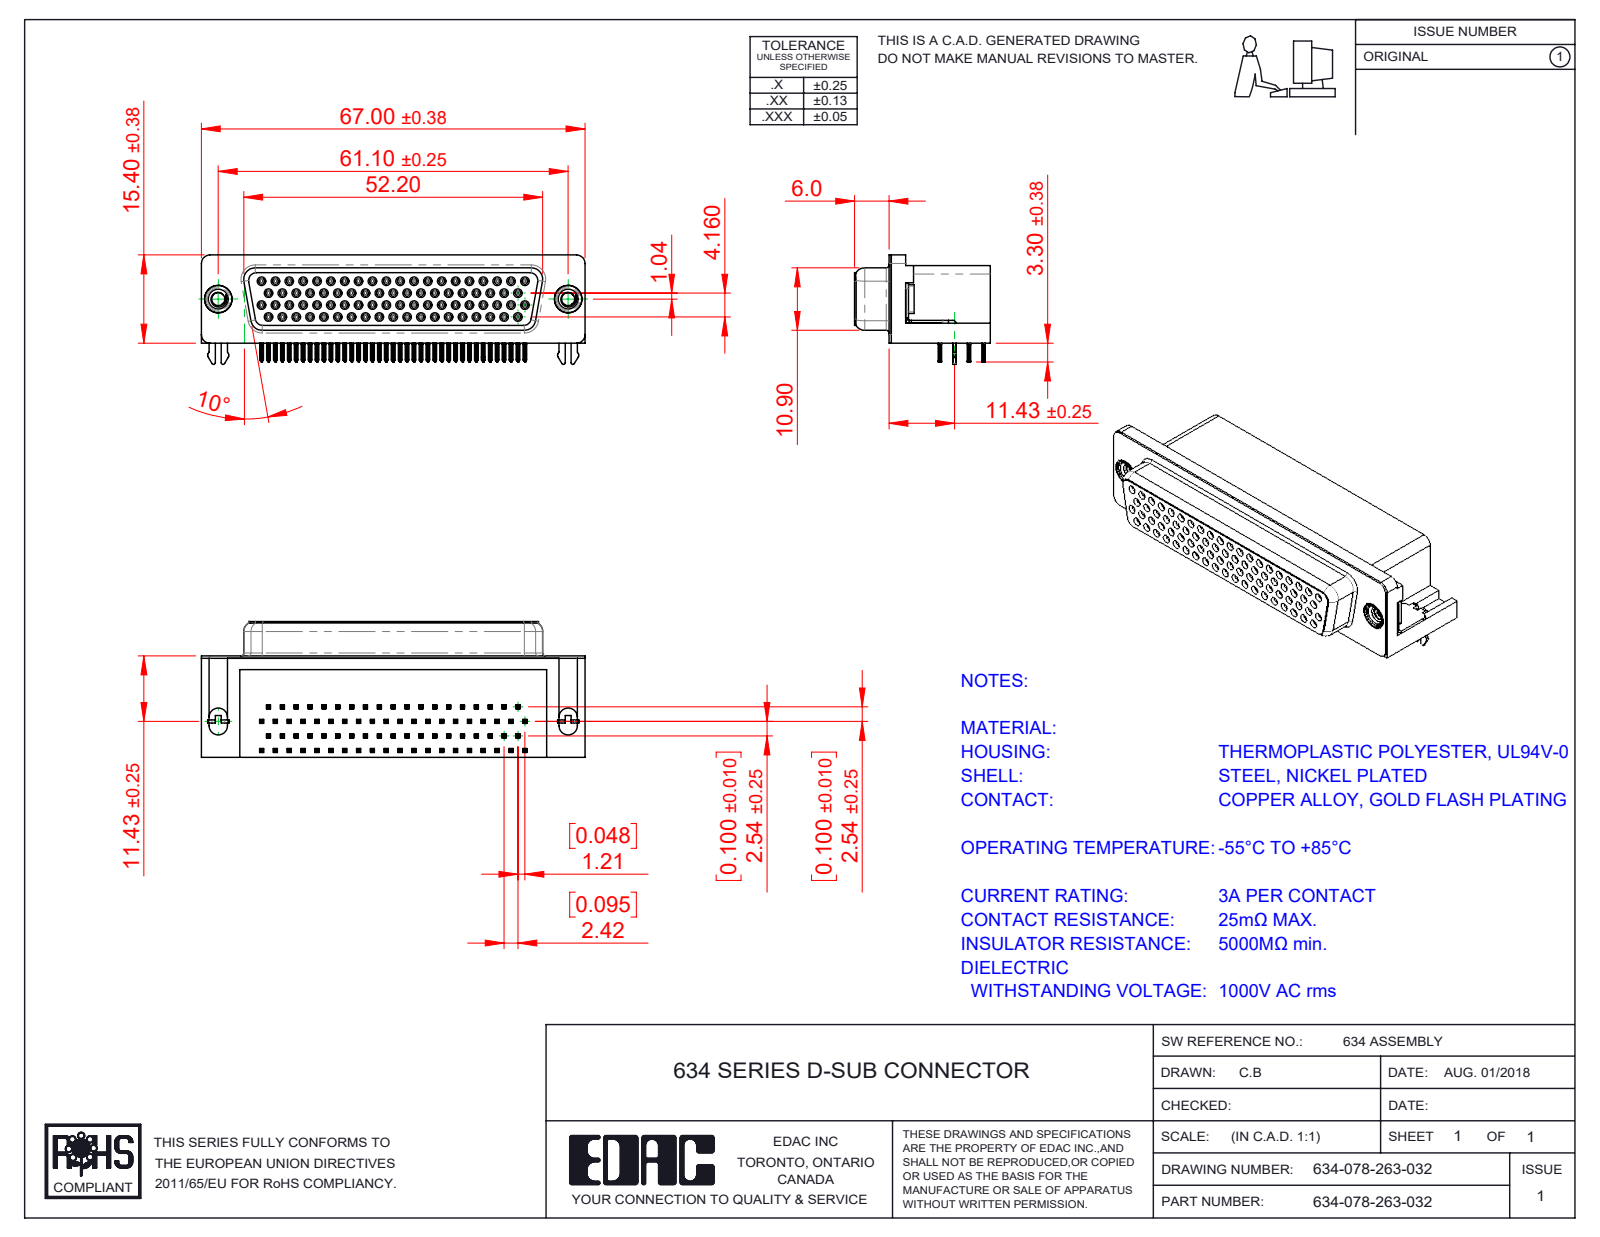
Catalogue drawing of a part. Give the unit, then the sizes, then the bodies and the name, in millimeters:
Units: millimetres
Overall size (bounding box): 67 × 23.7 × 19.1
Round holes (diameter × count): ⌀0.8 ×78, ⌀0.9 ×78, ⌀2.26 ×2, ⌀4 ×2, ⌀4.8 ×2, ⌀5 ×2
Round bosses / shafts (diameter × count): ⌀1.2 ×78, ⌀4.9 ×2, ⌀4.75 ×2, ⌀3.9 ×2
Partial cylindrical surfaces — rounded edges, fillets, slot ends (radius × count): R0.1 ×624, R0.15 ×312, R0.35 ×156, R0.34 ×78, R1 ×20, R0.28 ×19, R0.5 ×10, R0.25 ×8
Main face-to-face distances: 0.4, 13.2, 17.3, 10.05, 9.65, 0.85, 2.54, 1.25, 2.08, 3.1
Hole centre spacings: 8.72, 2.41, 15.87, 23.08, 2.42, 6.4, 7.26, 8.37
Volume: 17 229 mm³ · Surface area: 21 992 mm²
Bodies: 84 solids, 11386 faces (5123 planar, 2539 cylindrical, 3724 other)
Part name (STEP PRODUCT): Contact Bottom_78 Socket; Contact Top 78; 634 Shell_78 Socket; 2 Prong Board Lock_78 Socket (+6 more)
STEP written by: SolidWorks 2016 (CONFIG_CONTROL_DESIGN)
